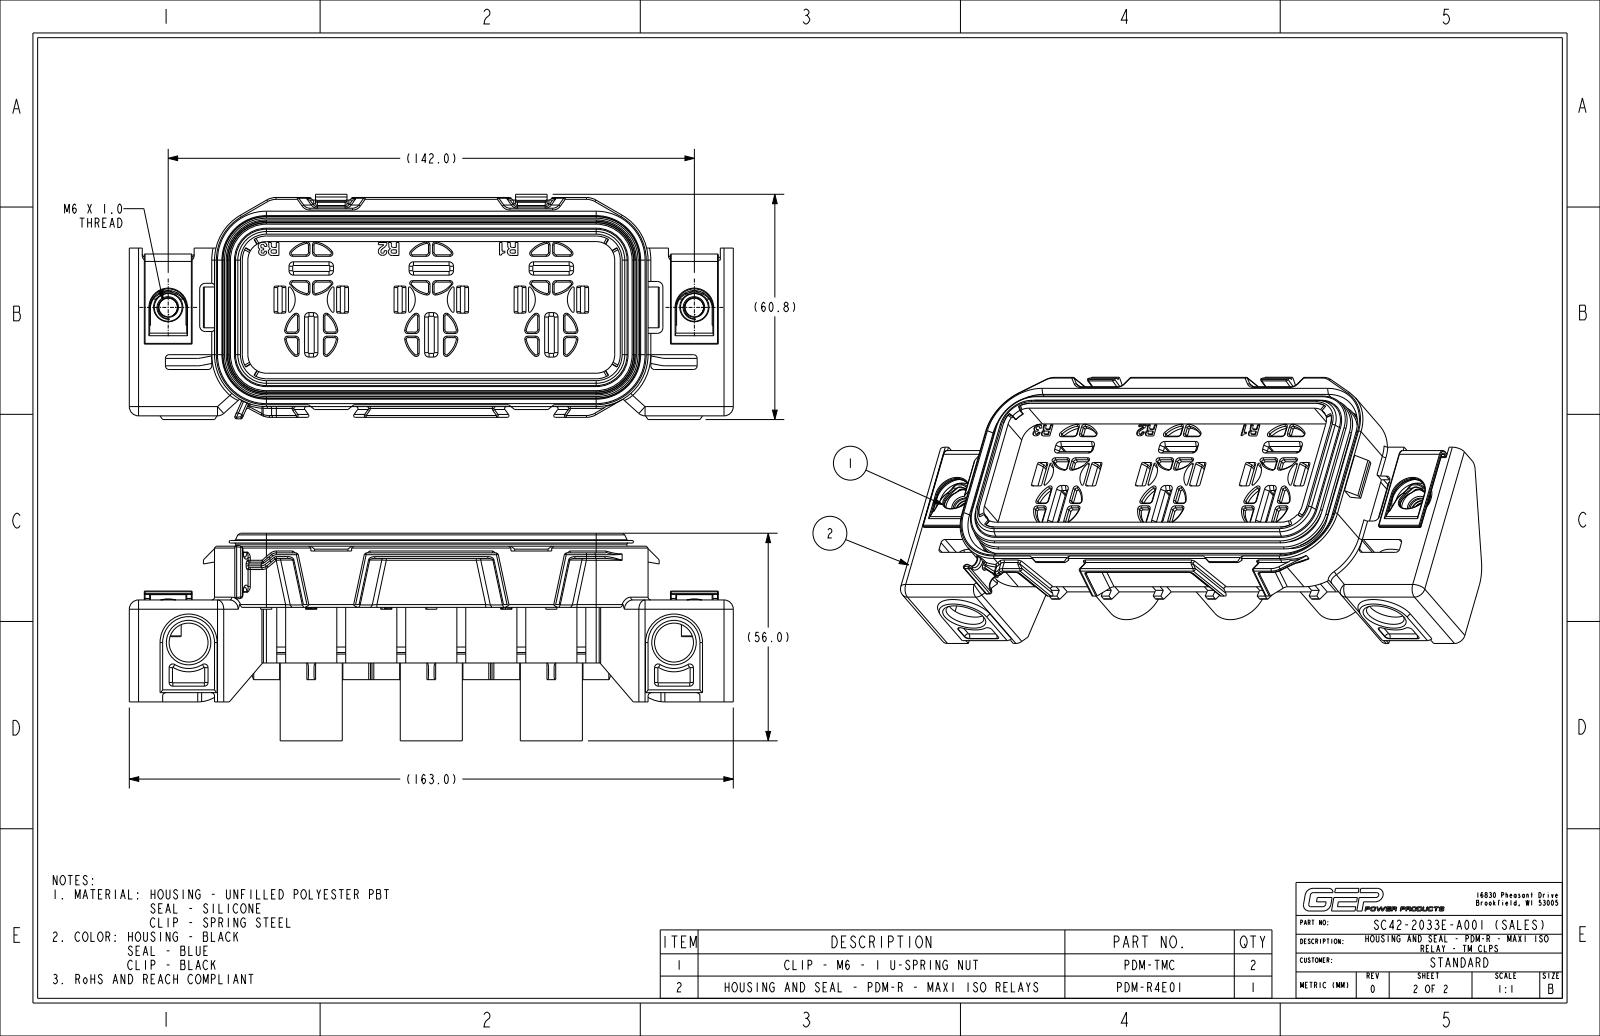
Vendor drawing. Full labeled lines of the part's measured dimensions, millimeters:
Part name (STEP PRODUCT): C26-1012-2E_SALES_NCF; C14-1013_INSTALLED_NCF; PDM-RS_INSTALLED_NCF_ASM; PDM-R4E01_NCF_ASM (+3 more)
STEP written by: CREO PARAMETRIC BY PTC INC, 2024014 (CONFIG_CONTROL_DESIGN)
Units: millimetres
Bodies: 4 solids, 3291 faces (1448 planar, 958 cylindrical, 885 other)
Overall size (bounding box): 163 × 60.76 × 56
Volume: 120 492 mm³ · Surface area: 108 156 mm²
Round holes (diameter × count): ⌀9.8 ×6, ⌀13.75 ×6, ⌀10.5 ×4, ⌀5 ×2, ⌀7.5 ×2, ⌀12.5 ×2
Round bosses / shafts (diameter × count): ⌀16.75 ×3, ⌀7 ×2, ⌀5 ×1, ⌀2.5 ×1
Partial cylindrical surfaces — rounded edges, fillets, slot ends (radius × count): R0.5 ×237, R0.2 ×92, R0.3 ×82, R0.4 ×76, R0.9 ×39, R1 ×26, R0.6 ×24, R0.35 ×16
Main face-to-face distances: 2, 1.5, 38.5, 37, 9.5, 11.5, 1.8, 5.5, 9, 7
Hole centre spacings: 32.4, 12.47, 13.24, 24.66, 25.05, 37.02, 42.46, 42.69
